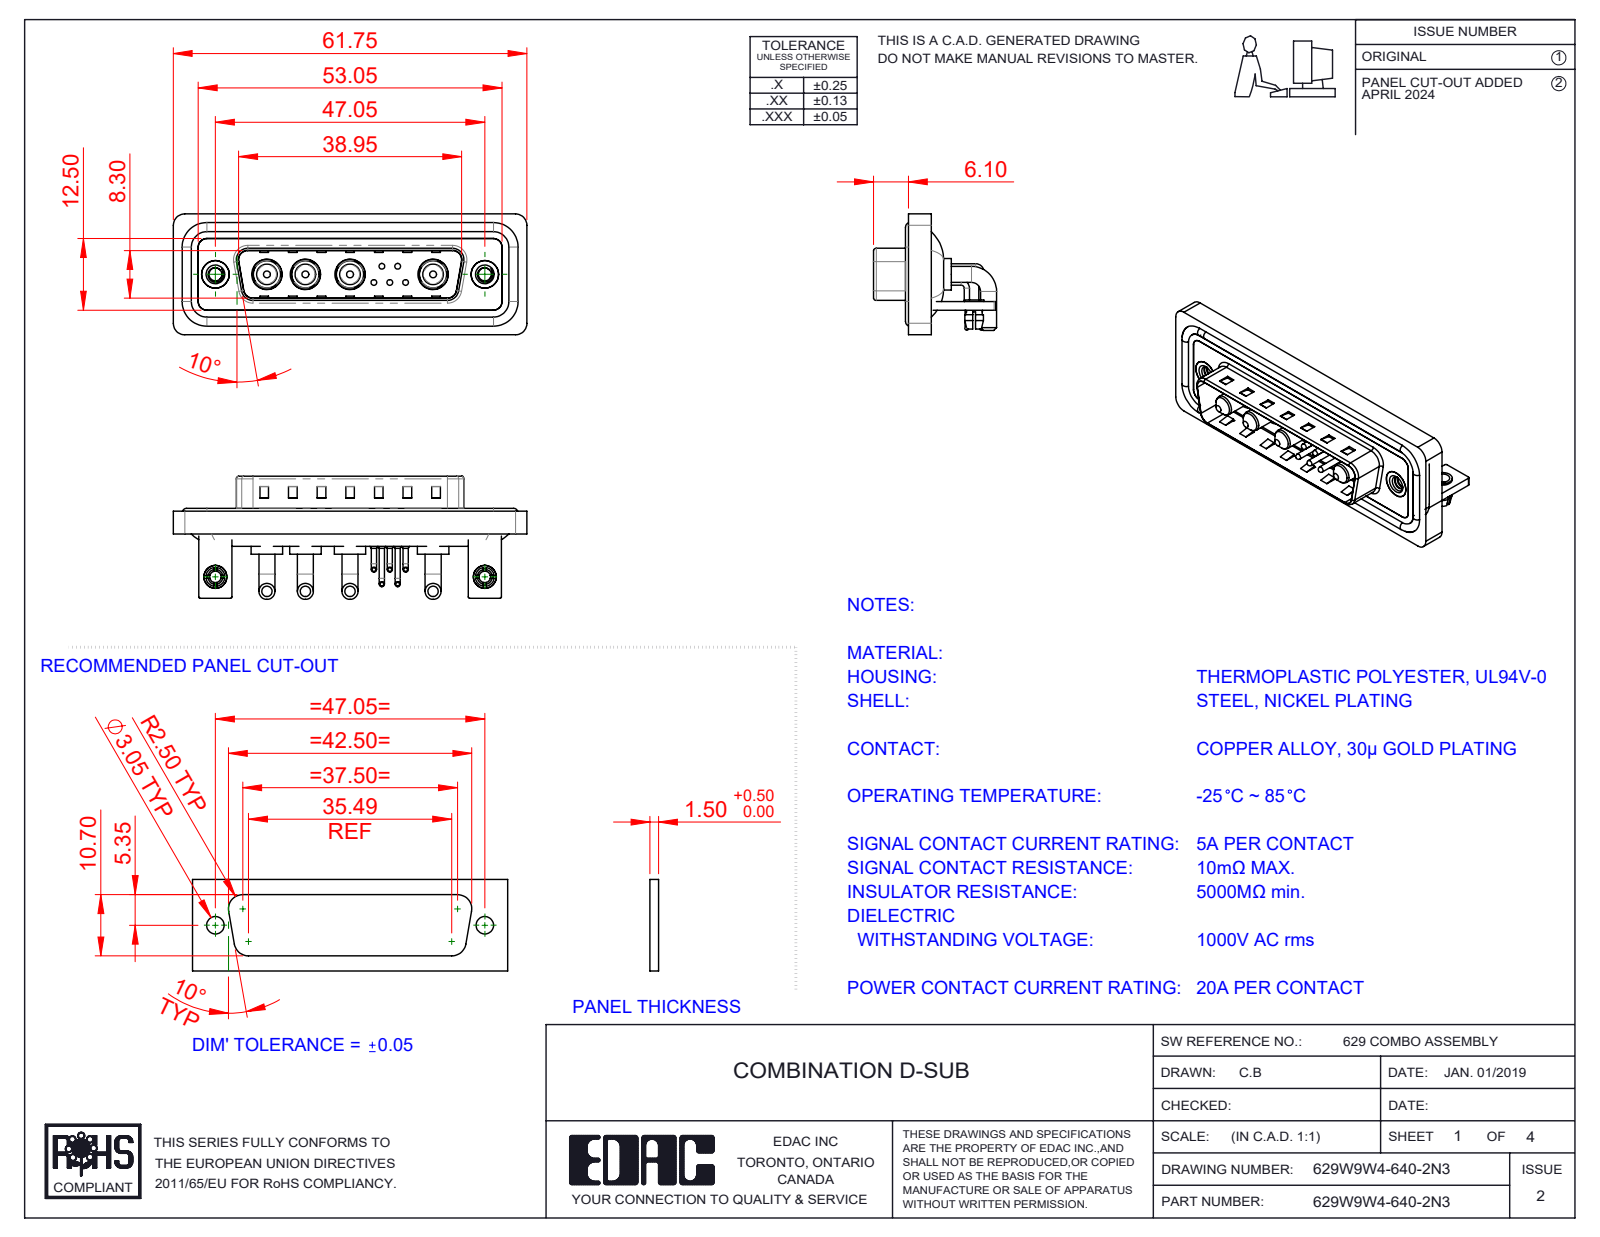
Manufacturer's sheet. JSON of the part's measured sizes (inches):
{"part_name": "629Combo Contact Row 1; 629Combo Waterproof Housing_25 Contacts; 629Combo Board Lock; 629Combo Shell Rear_25 Contacts (+7 more)", "step_written_by": "SolidWorks 2023 (CONFIG_CONTROL_DESIGN)", "units": "inches", "bodies": {"solids": 24, "faces": 1337, "planar": 637, "cylindrical": 502, "other": 198}, "overall_size": [2.431, 0.846, 0.831], "volume_in3": 0.489, "surface_area_in2": 20.42, "round_holes": [[0.079, 7], [0.03, 5], [0.063, 5], [0.191, 4], [0.209, 4], [0.089, 2], [0.098, 2], [0.126, 2], [0.157, 2], [0.189, 2], [0.197, 2]], "round_bosses_or_shafts": [[0.035, 10], [0.11, 8], [0.059, 5], [0.039, 5], [0.026, 5], [0.217, 4], [0.205, 4], [0.187, 4]], "partial_cylinders_radius": [[0.079, 19], [0.059, 18], [0.01, 16], [0.02, 9], [0.063, 8], [0.04, 5], [0.024, 4], [0.026, 4]], "face_to_face_distances": [0.016, 0.059, 0.031, 0.114, 0.083, 0.043, 0.146, 0.161, 0.177, 0.063], "hole_center_spacings": [0.124, 0.109, 0.198, 0.571, 1.852, 0.109, 0.173, 0.174]}
